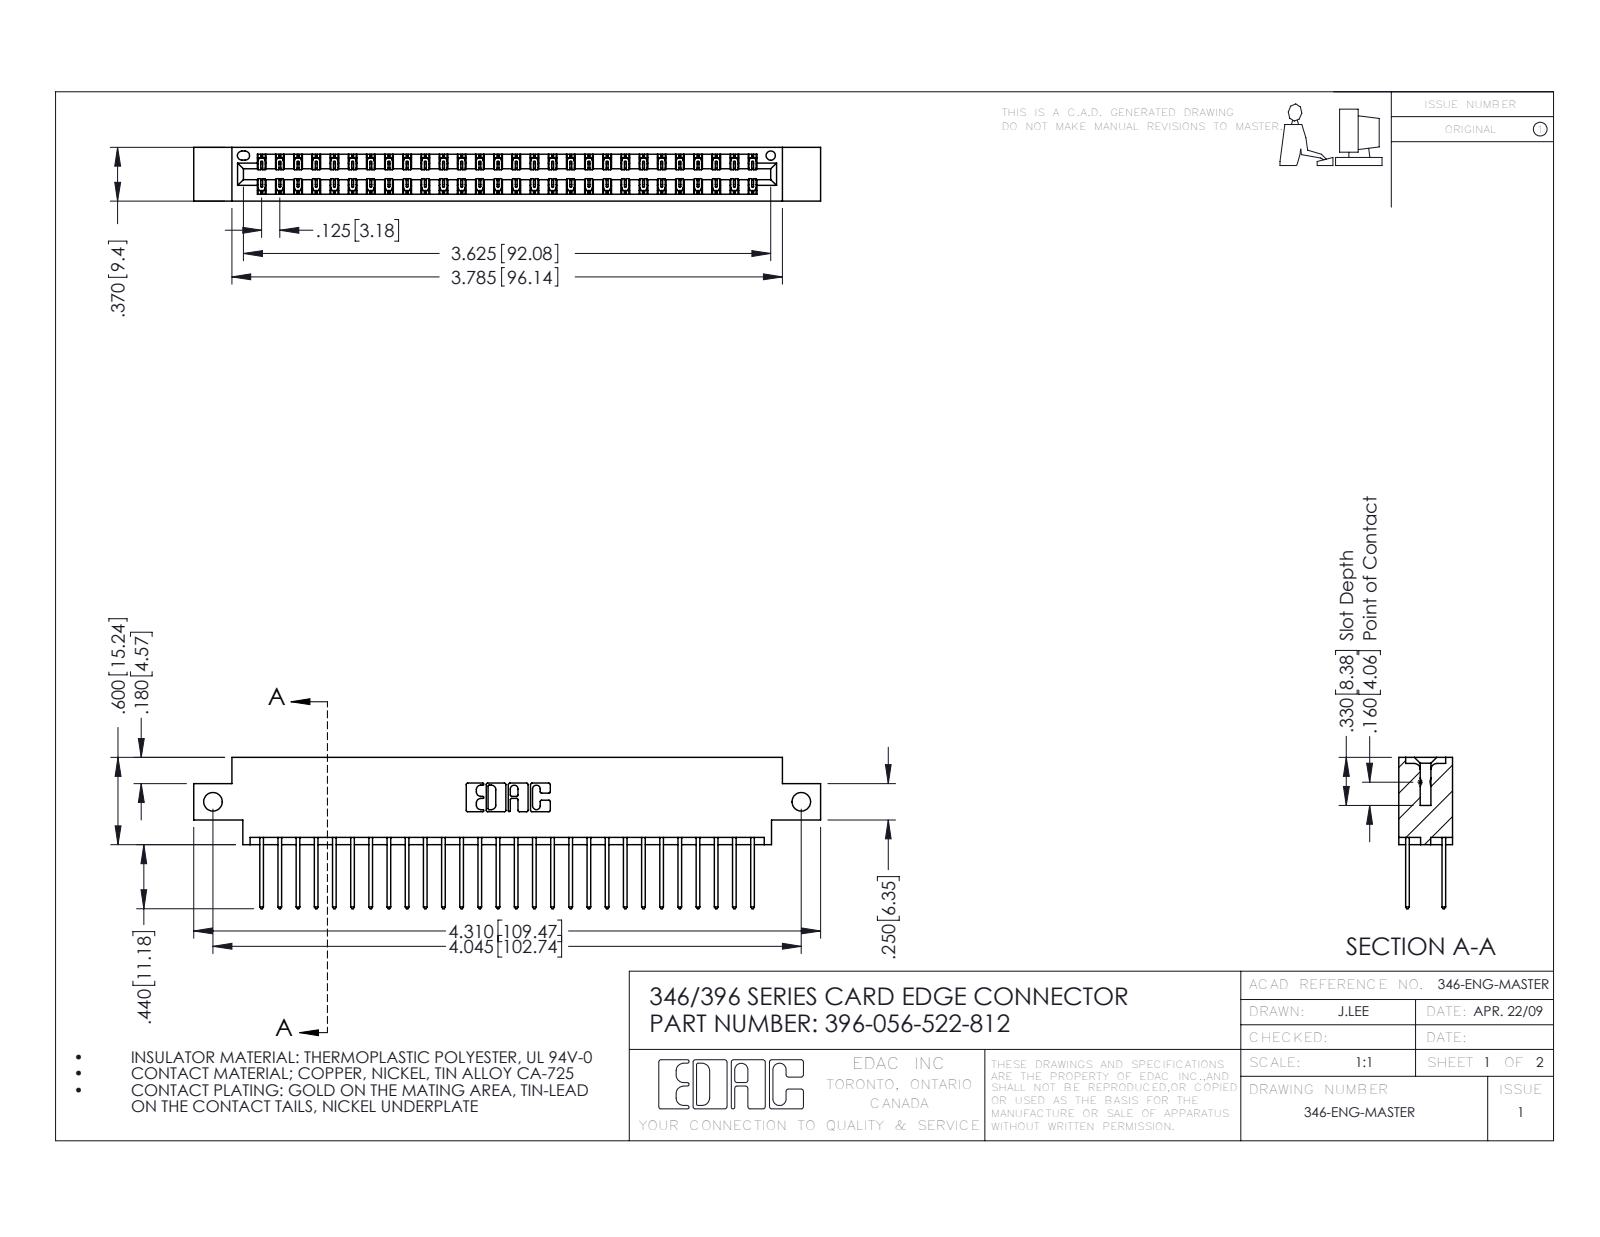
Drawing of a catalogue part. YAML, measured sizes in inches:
part_name: "346 Part_0.170 Offset - Side Mount; 396-056-522-812; 345-292-001_345-293-122"
step_written_by: "SolidWorks 2016 (CONFIG_CONTROL_DESIGN)"
units: inches
bodies: {solids: 57, faces: 3038, planar: 2040, cylindrical: 998, other: 0}
overall_size: [4.31, 1.04, 0.37]
volume: 0.639
surface_area: 23.06
round_holes:
  - {diameter: 0.128, count: 2}
  - {diameter: 0.064, count: 1}
partial_cylinders:
  - {radius: 0.006, count: 84}
  - {radius: 0.01, count: 56}
  - {radius: 0.01, count: 22}
  - {radius: 0.007, count: 6}
  - {radius: 0.031, count: 6}
  - {radius: 0.026, count: 3}
  - {radius: 0.014, count: 2}
  - {radius: 0.022, count: 2}
face_to_face_distances: [0.048, 0.322, 0.25, 0.37, 0.072, 0.298, 0.025, 0.275, 0.148, 0.222]
hole_center_spacings: [4.045]
